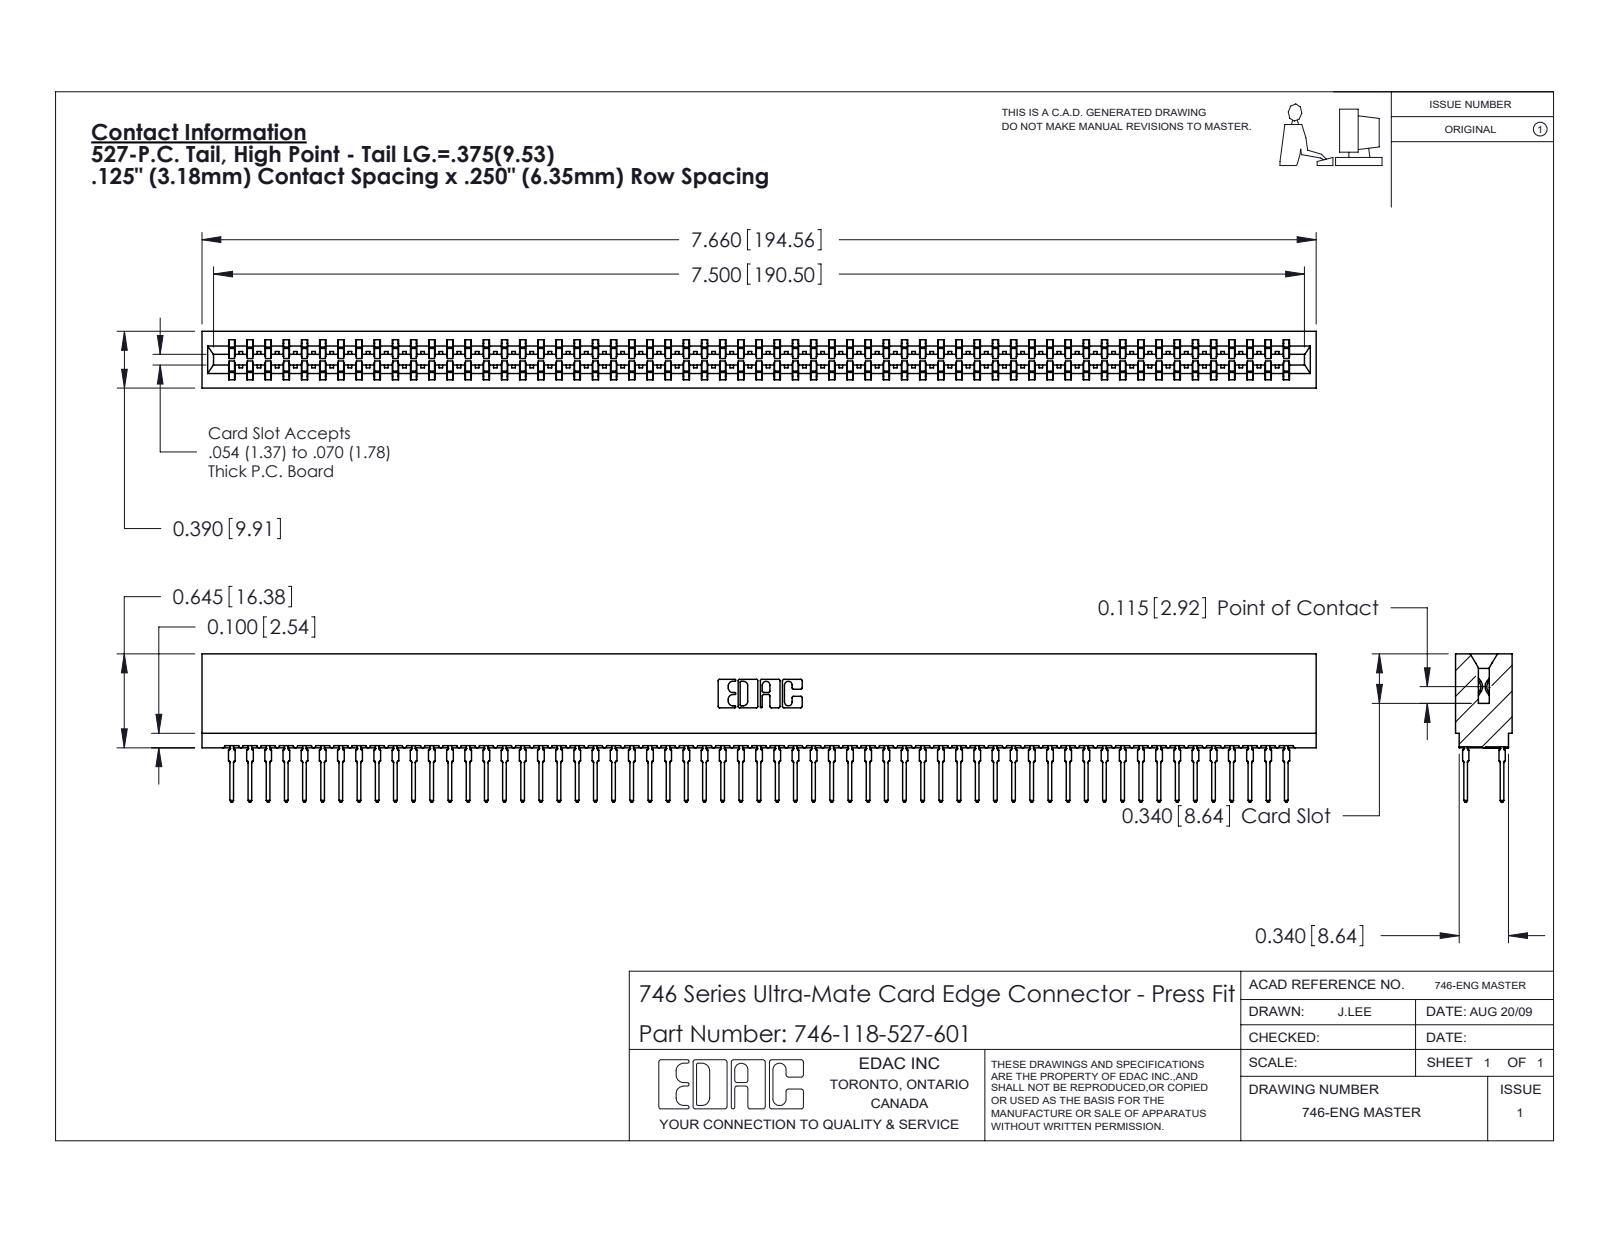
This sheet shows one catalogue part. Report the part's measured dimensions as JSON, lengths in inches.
{"part_name": "746 Part_.340 Slot Depth - 01; 746-292-001_527; 746-118-527-601", "step_written_by": "SolidWorks 2020 (CONFIG_CONTROL_DESIGN)", "units": "inches", "bodies": {"solids": 119, "faces": 10658, "planar": 5483, "cylindrical": 2107, "other": 3068}, "overall_size": [7.66, 1.019, 0.39], "volume_in3": 1.371, "surface_area_in2": 53.01, "partial_cylinders_radius": [[0.021, 236], [0.015, 60], [0.01, 22], [0.005, 8], [0.011, 8], [0.007, 6], [0.031, 6], [0.026, 3]], "face_to_face_distances": [0.057, 0.333, 0.39, 0.025, 0.25, 0.307, 0.275, 0.083, 0.015, 0.059]}
